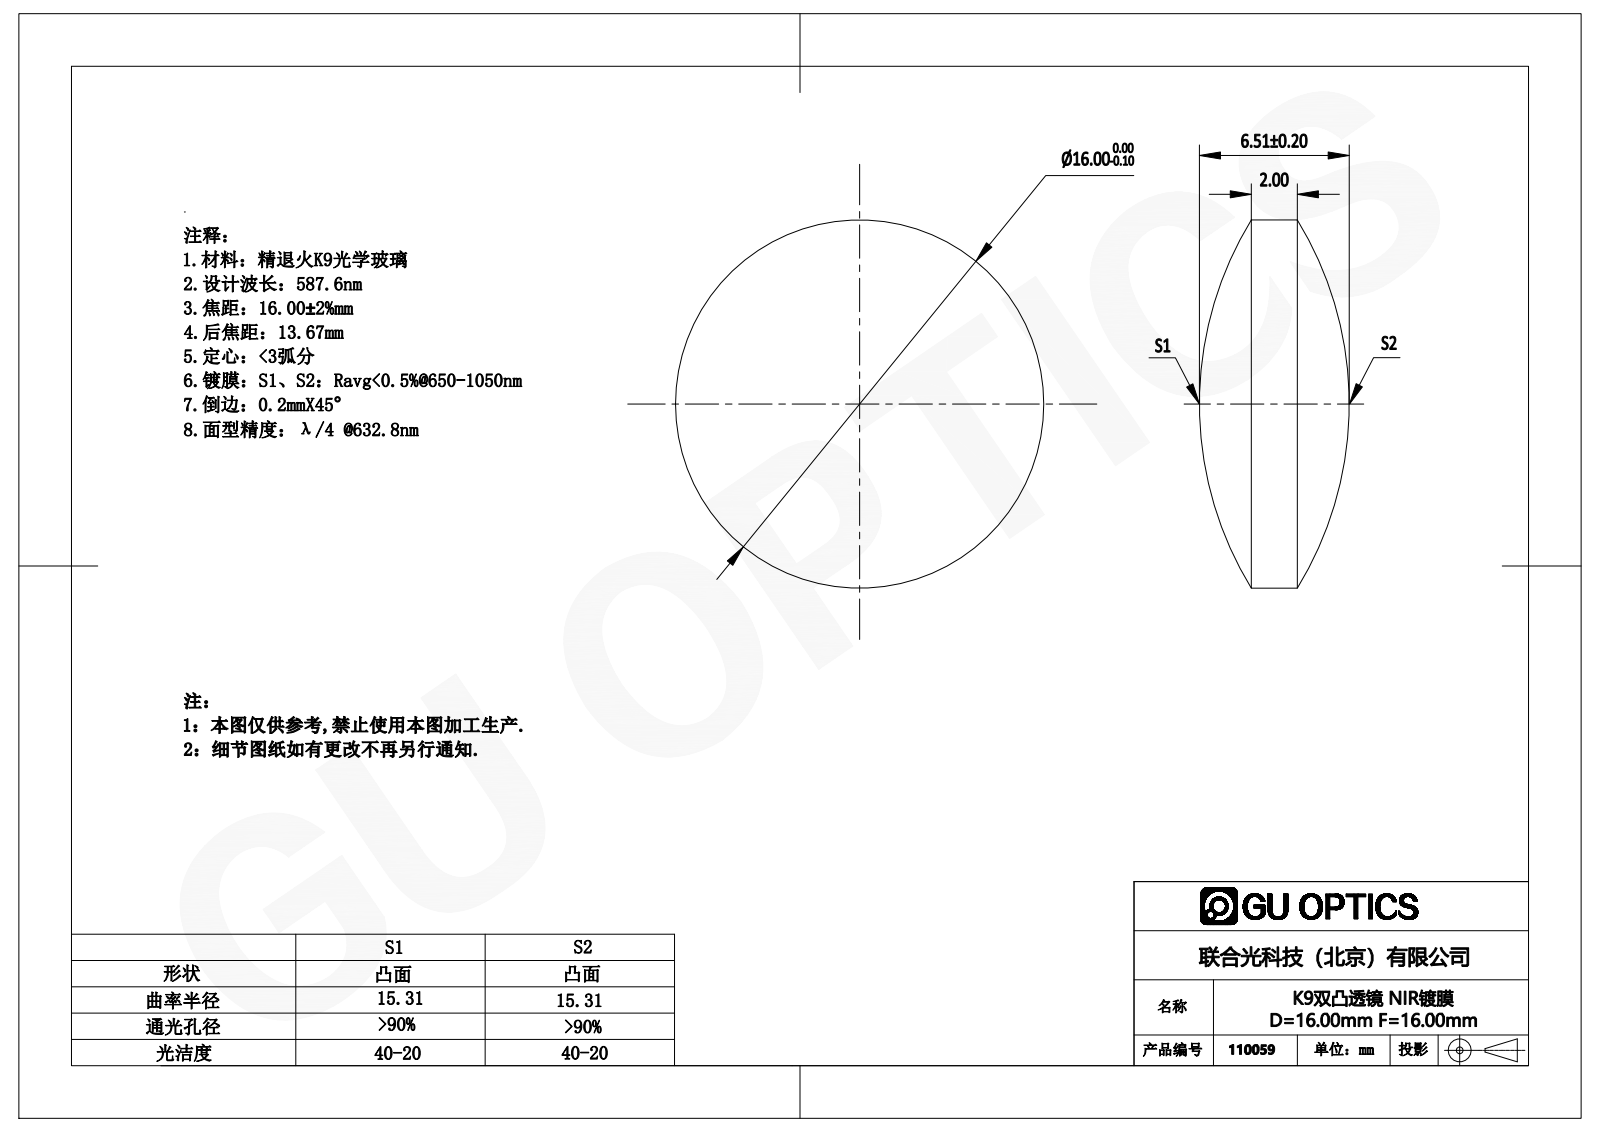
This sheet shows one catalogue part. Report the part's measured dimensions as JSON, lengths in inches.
{"part_name": "110015", "step_written_by": "SolidWorks 2016 (CONFIG_CONTROL_DESIGN)", "units": "inches", "bodies": {"solids": 1, "faces": 6, "planar": 0, "cylindrical": 2, "other": 4}, "overall_size": [0.63, 0.63, 0.256], "volume_in3": 0.053, "surface_area_in2": 0.829, "round_bosses_or_shafts": [[0.63, 1]]}
